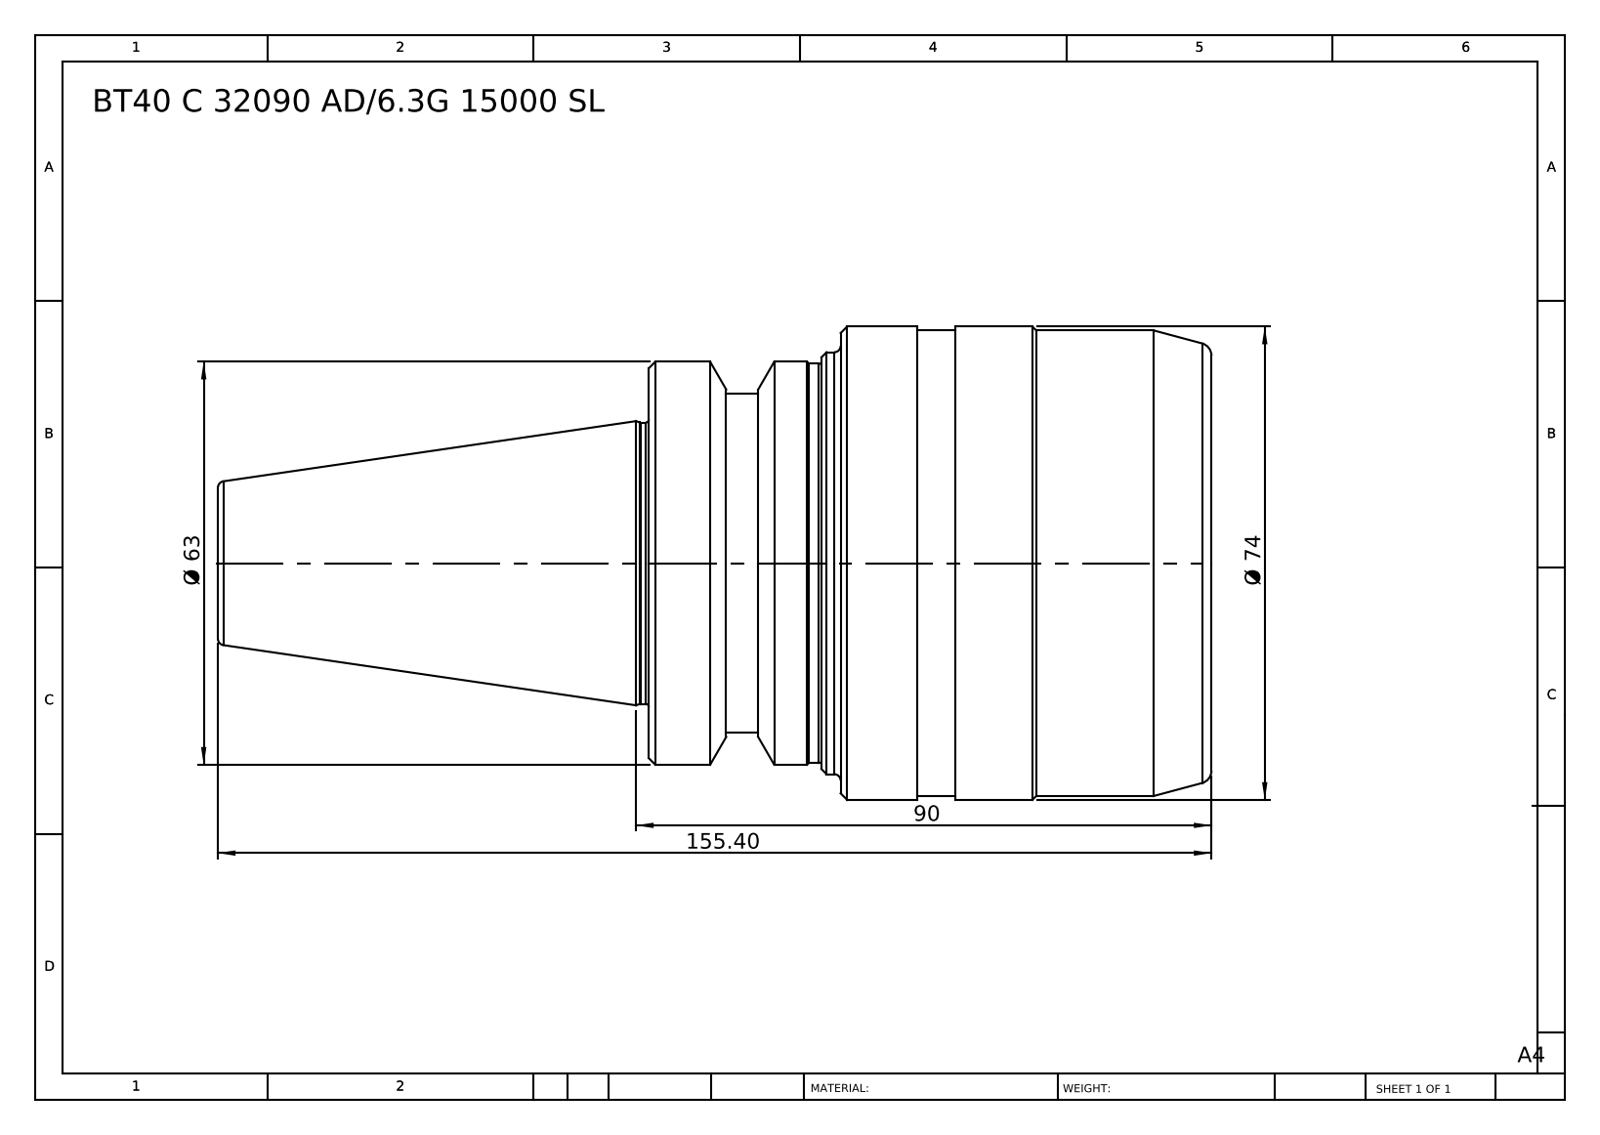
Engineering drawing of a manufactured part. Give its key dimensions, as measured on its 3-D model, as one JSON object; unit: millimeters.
{"part_name": "BT40 C32 090 AD-6.3G 15000 SL", "step_written_by": "SolidWorks 2014 (CONFIG_CONTROL_DESIGN)", "units": "millimeters", "bodies": {"solids": 1, "faces": 61, "planar": 9, "cylindrical": 20, "other": 32}, "overall_size": [155.4, 74, 74], "volume_mm3": 396961, "surface_area_mm2": 34532, "round_bosses_or_shafts": [[74, 1], [72.8, 1], [66, 1], [63, 1], [62.5, 1], [53, 1], [44, 1]], "face_to_face_distances": [88, 58, 30, 155.4, 97.4, 67.4, 61, 3, 27, 94.4]}
